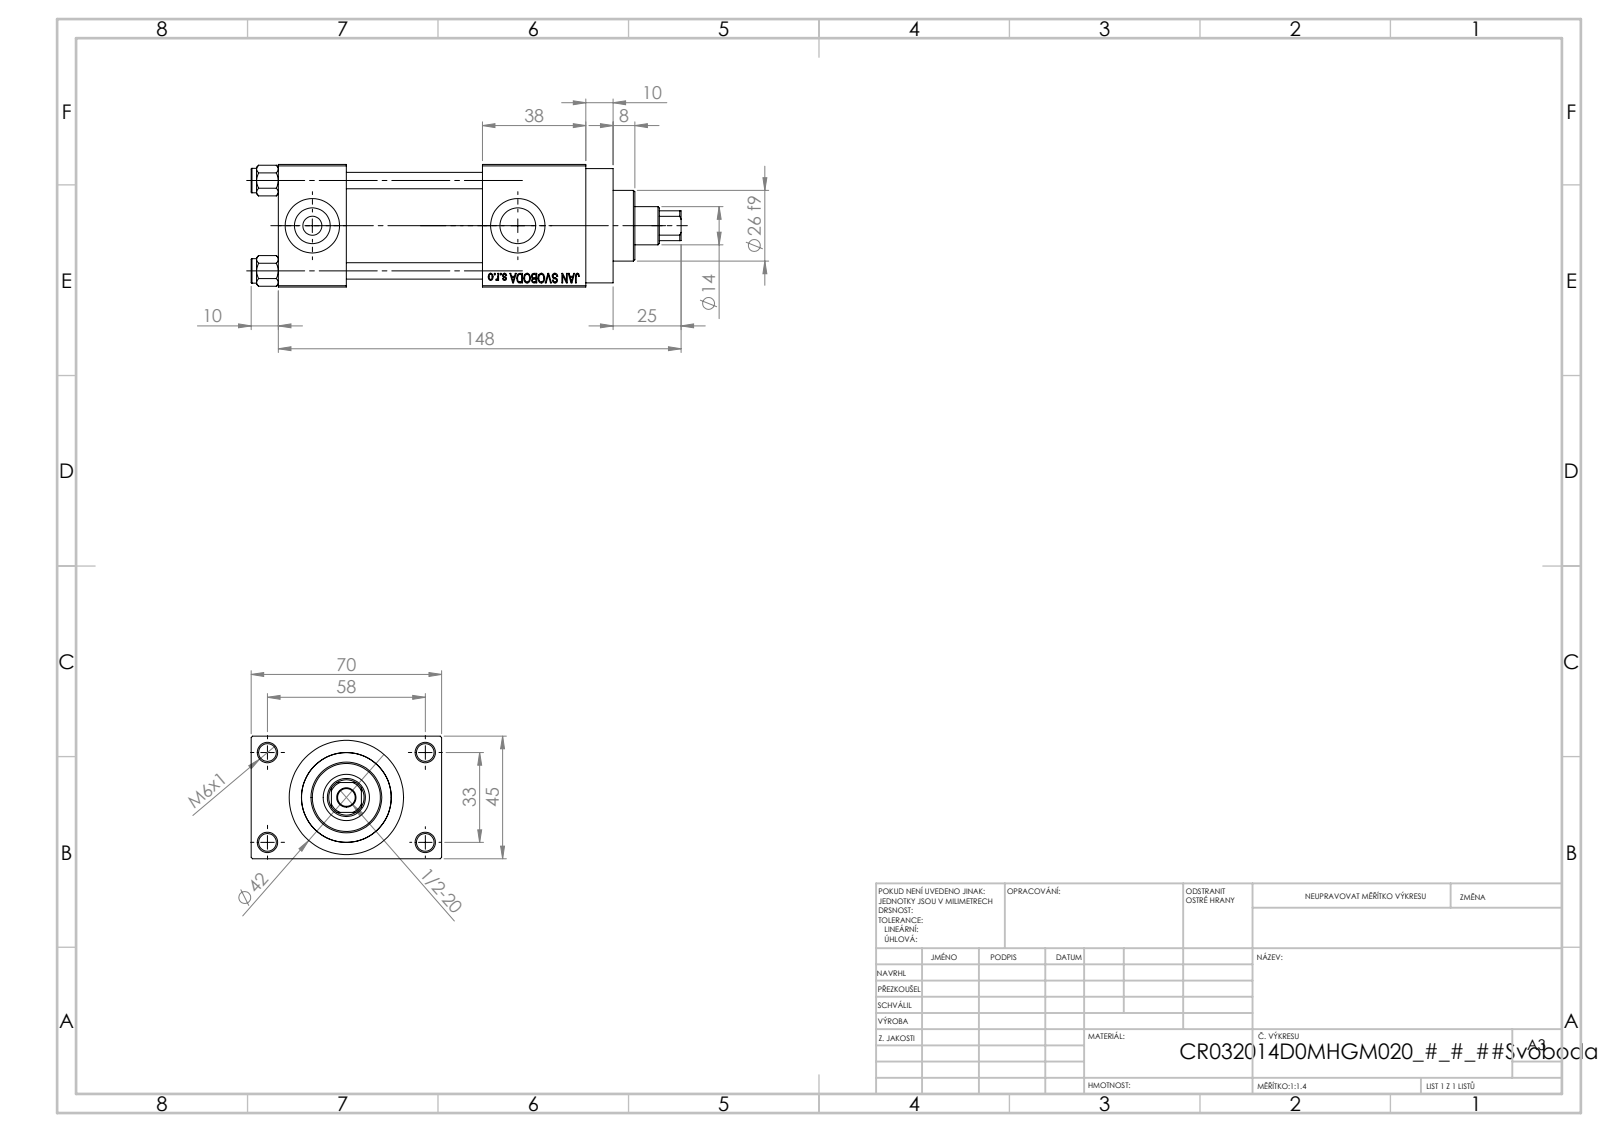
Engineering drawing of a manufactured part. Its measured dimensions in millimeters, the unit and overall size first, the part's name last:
Units: millimetres
Overall size (bounding box): 158 × 70 × 45
Round holes (diameter × count): ⌀6.5 ×5, ⌀6 ×4, ⌀7 ×2, ⌀13.16 ×2, ⌀20 ×2, ⌀14 ×1, ⌀17 ×1, ⌀24 ×1, ⌀32 ×1, ⌀33 ×1
Round bosses / shafts (diameter × count): ⌀9 ×4, ⌀42 ×1, ⌀38 ×1, ⌀26 ×1
Partial cylindrical surfaces — rounded edges, fillets, slot ends (radius × count): R6.5 ×1
Main face-to-face distances: 45, 25, 50, 12.5, 75, 57.5, 88, 38, 113, 70
Hole centre spacings: 12.4, 23.48, 33.2, 33.37, 35.35, 45.6, 56.35, 33
Volume: 230 327 mm³ · Surface area: 75 388 mm²
Bodies: 11 solids, 1102 faces (496 planar, 88 cylindrical, 518 other)
Part name (STEP PRODUCT): V215CR_D_Body; NUT_M5_D; V215_VC_A; V215CR_D_TYCINKA (+1 more)
STEP written by: SolidWorks 2019 (CONFIG_CONTROL_DESIGN)
